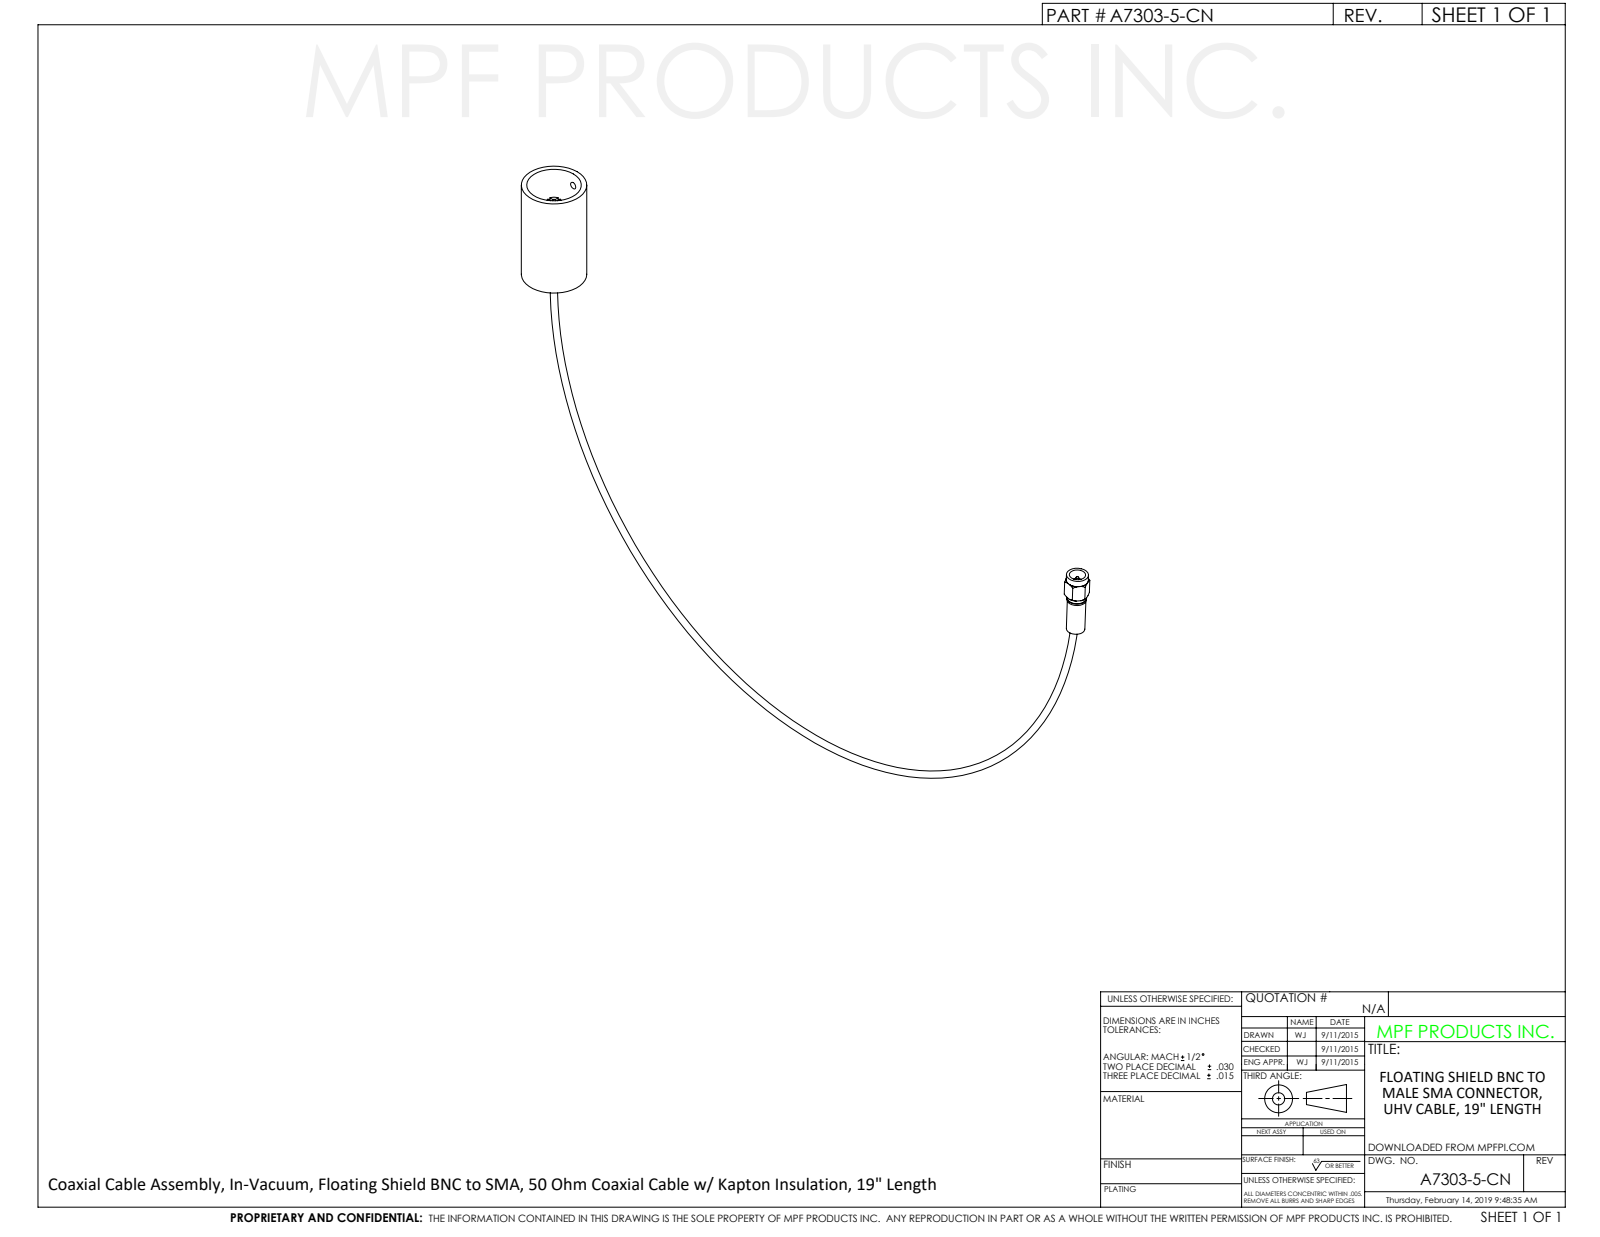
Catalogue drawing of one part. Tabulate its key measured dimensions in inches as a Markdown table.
| quantity | value |
| --- | --- |
| part name | A7303-5-CN |
| STEP written by | SolidWorks 2012 (CONFIG_CONTROL_DESIGN) |
| units | inches |
| bodies | 1 solid, 71 faces (38 planar, 26 cylindrical, 7 other) |
| overall size | 11.11 × 6.833 × 1 |
| volume | 1.16 in³ |
| surface area | 16.55 in² |
| round holes (diameter × count) | 0.1 × 3, 0.2 × 1, 0.609 × 1, 0.75 × 1 |
| round bosses / shafts (diameter × count) | 1 × 1, 0.669 × 1, 0.2 × 1, 0.1 × 1 |
| main face-to-face distances | 1.5, 0.712, 0.3, 0.712, 0.1, 0.165, 0.4, 0.5, 0.2, 0.165 |
| hole center spacings | 0.35 |
